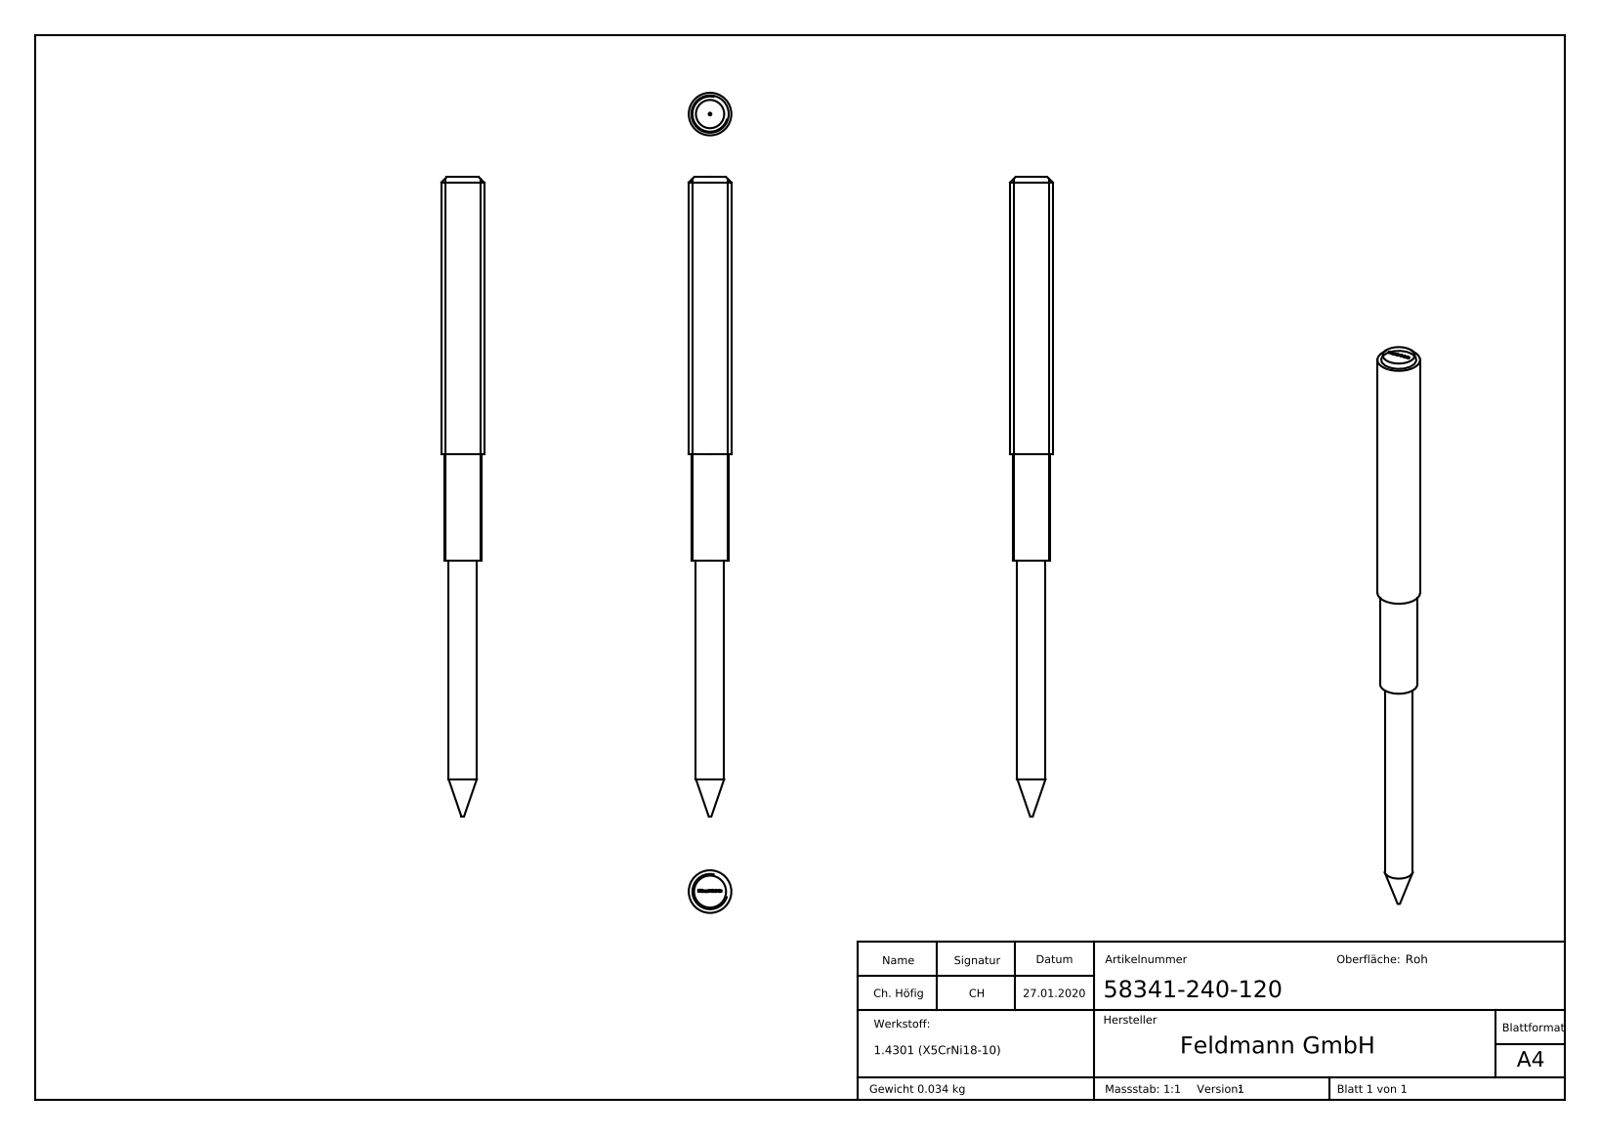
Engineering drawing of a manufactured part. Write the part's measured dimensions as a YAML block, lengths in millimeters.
part_name: "58341-240-120"
step_written_by: "SolidWorks 2015 (CONFIG_CONTROL_DESIGN)"
units: millimeters
bodies: {solids: 1, faces: 265, planar: 132, cylindrical: 3, other: 130}
overall_size: [120, 8, 8]
volume: 4333
surface_area: 2562
round_bosses_or_shafts:
  - {diameter: 8, count: 1}
  - {diameter: 7, count: 1}
  - {diameter: 5.3, count: 1}
face_to_face_distances: [72, 20, 52, 71.9, 51.9, 48, 68, 119.9, 120, 2.35]
